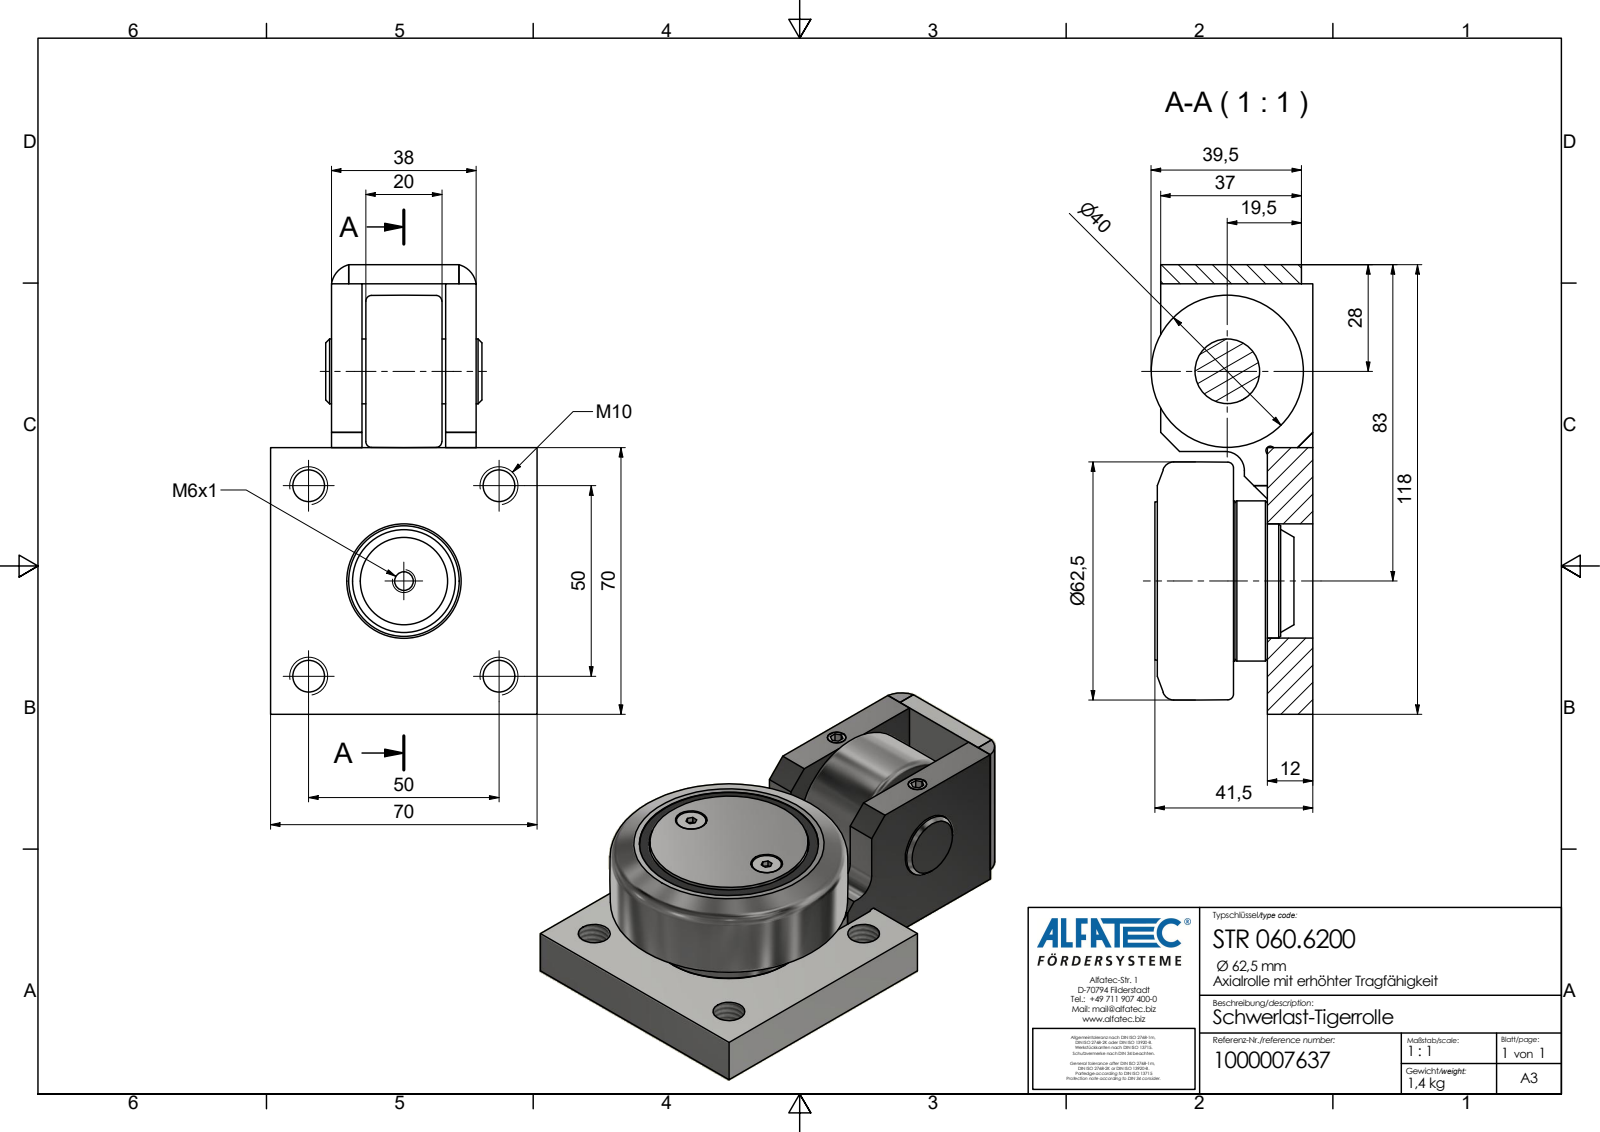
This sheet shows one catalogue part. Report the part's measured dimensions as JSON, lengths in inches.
{"part_name": "STR 060.6200_Kontur", "step_written_by": "Autodesk Inventor 2020 (AP242_MANAGED_MODEL_BASED_3D_ENGINEERING_MIM_LF)", "units": "inches", "bodies": {"solids": 2, "faces": 367, "planar": 217, "cylindrical": 118, "other": 32}, "overall_size": [4.646, 2.756, 1.673], "volume_in3": 11.17, "surface_area_in2": 84.54, "round_holes": [[0.33, 4], [0.194, 3], [0.118, 2], [0.327, 2], [0.673, 1], [1.181, 1], [1.496, 1], [1.654, 1], [1.692, 1], [1.85, 1], [1.969, 1]], "round_bosses_or_shafts": [[0.157, 36], [0.307, 2], [1.791, 1], [1.772, 1], [1.657, 1], [1.634, 1], [1.457, 1], [0.669, 1]], "partial_cylinders_radius": [[0.243, 2], [0.047, 1], [0.197, 1]], "face_to_face_distances": [0.472, 1.181, 0.315, 0.984, 0.039, 0.827, 0.63, 0.945, 1.811, 2.126], "hole_center_spacings": [1.969, 1.075, 1.392, 1.824, 0.551, 1.245, 2.166, 2.244]}
